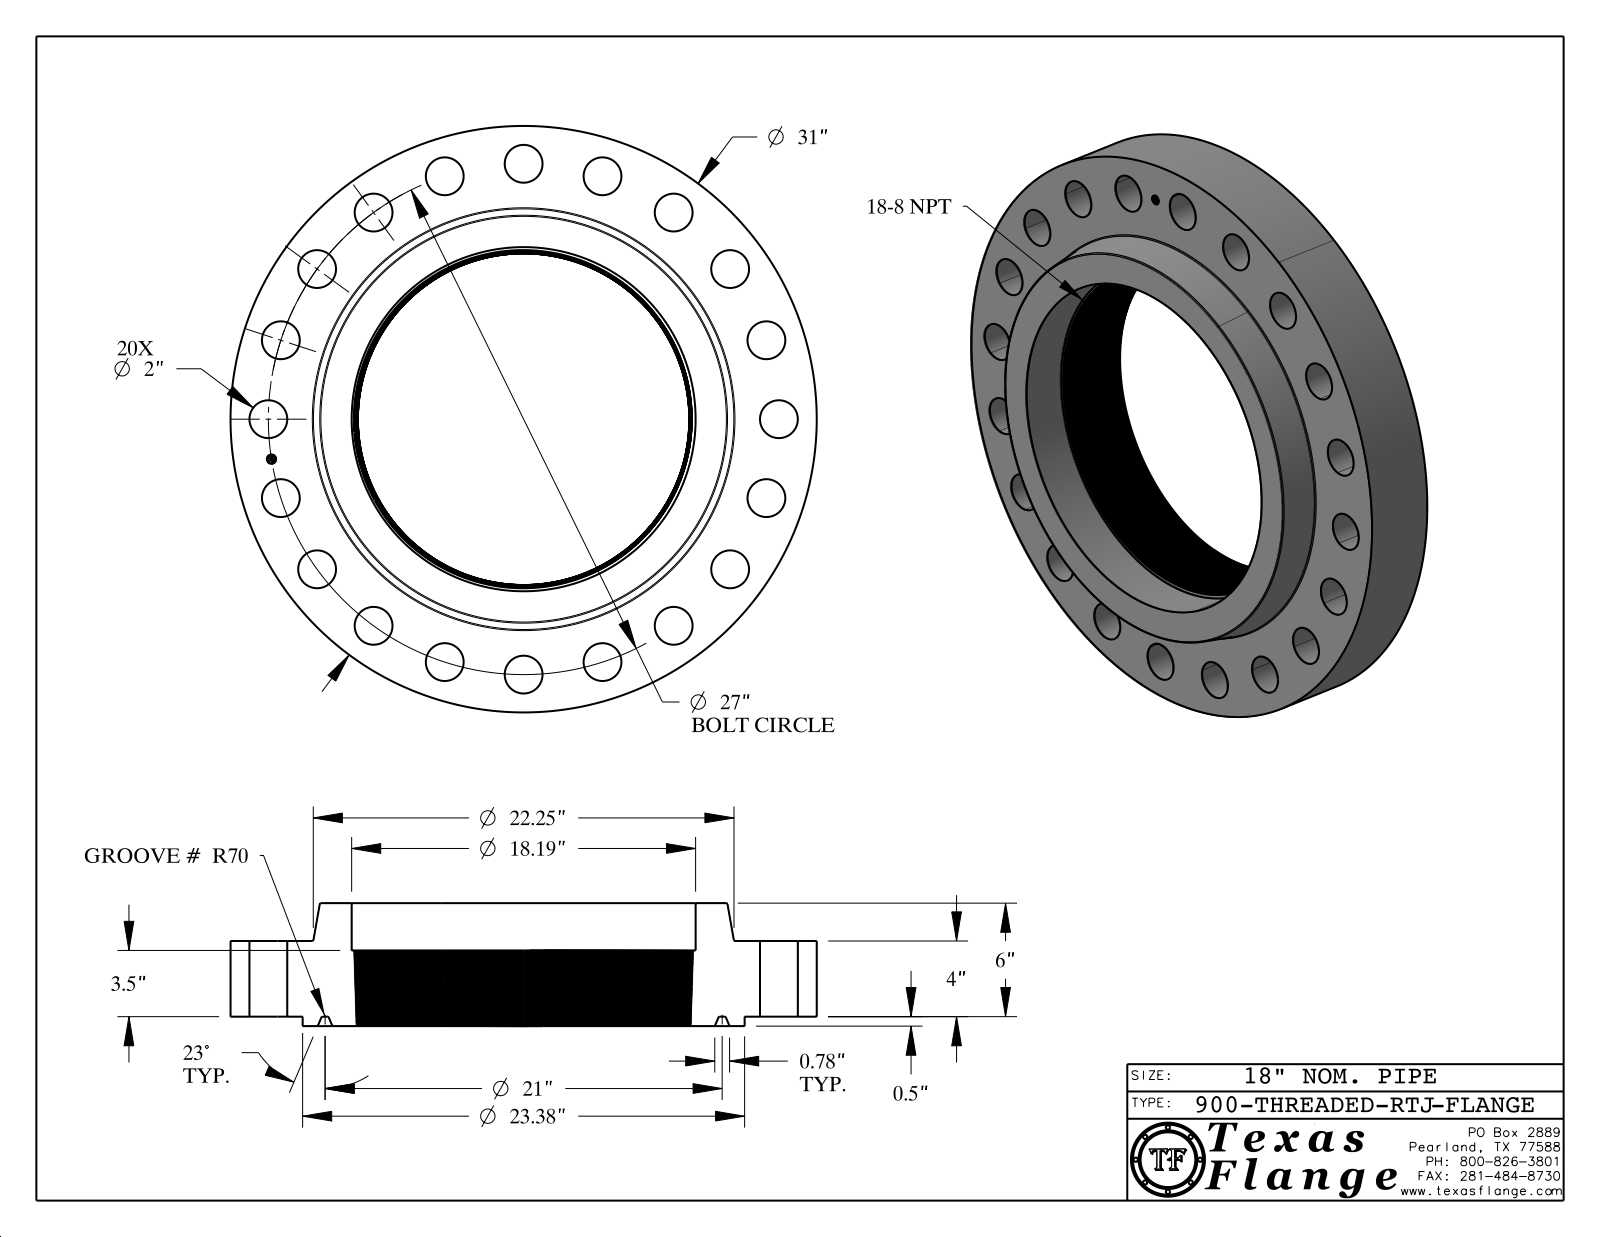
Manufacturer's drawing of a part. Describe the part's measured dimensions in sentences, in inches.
The part is named "900-THREADED-RTJ". Its 3-D file was written by "CATIA V5 STEP AP214 (AUTOMOTIVE_DESIGN)". It is 1 solid with 779 faces: 372 planar, 66 cylindrical and 341 other. Overall it measures 31 by 31 by 6.5 inches. Its volume is 2 077 cubic inches and its surface area 2 535 square inches. Round holes: 20 of diameter 2, 1 of diameter 0.495, 1 of diameter 18.19. Round bosses or shafts: 8 of diameter 0.03, 1 of diameter 31, 1 of diameter 23.375, 1 of diameter 0.39. The main face-to-face distances are 4, 0.5, 4.5, 6.5, 6, 2, 3.5, 2.5, 4.485, 3.985. The hole center spacings are 13.5, 21.843, 24.057, 25.678, 26.668, 4.224, 8.343, 12.258.
